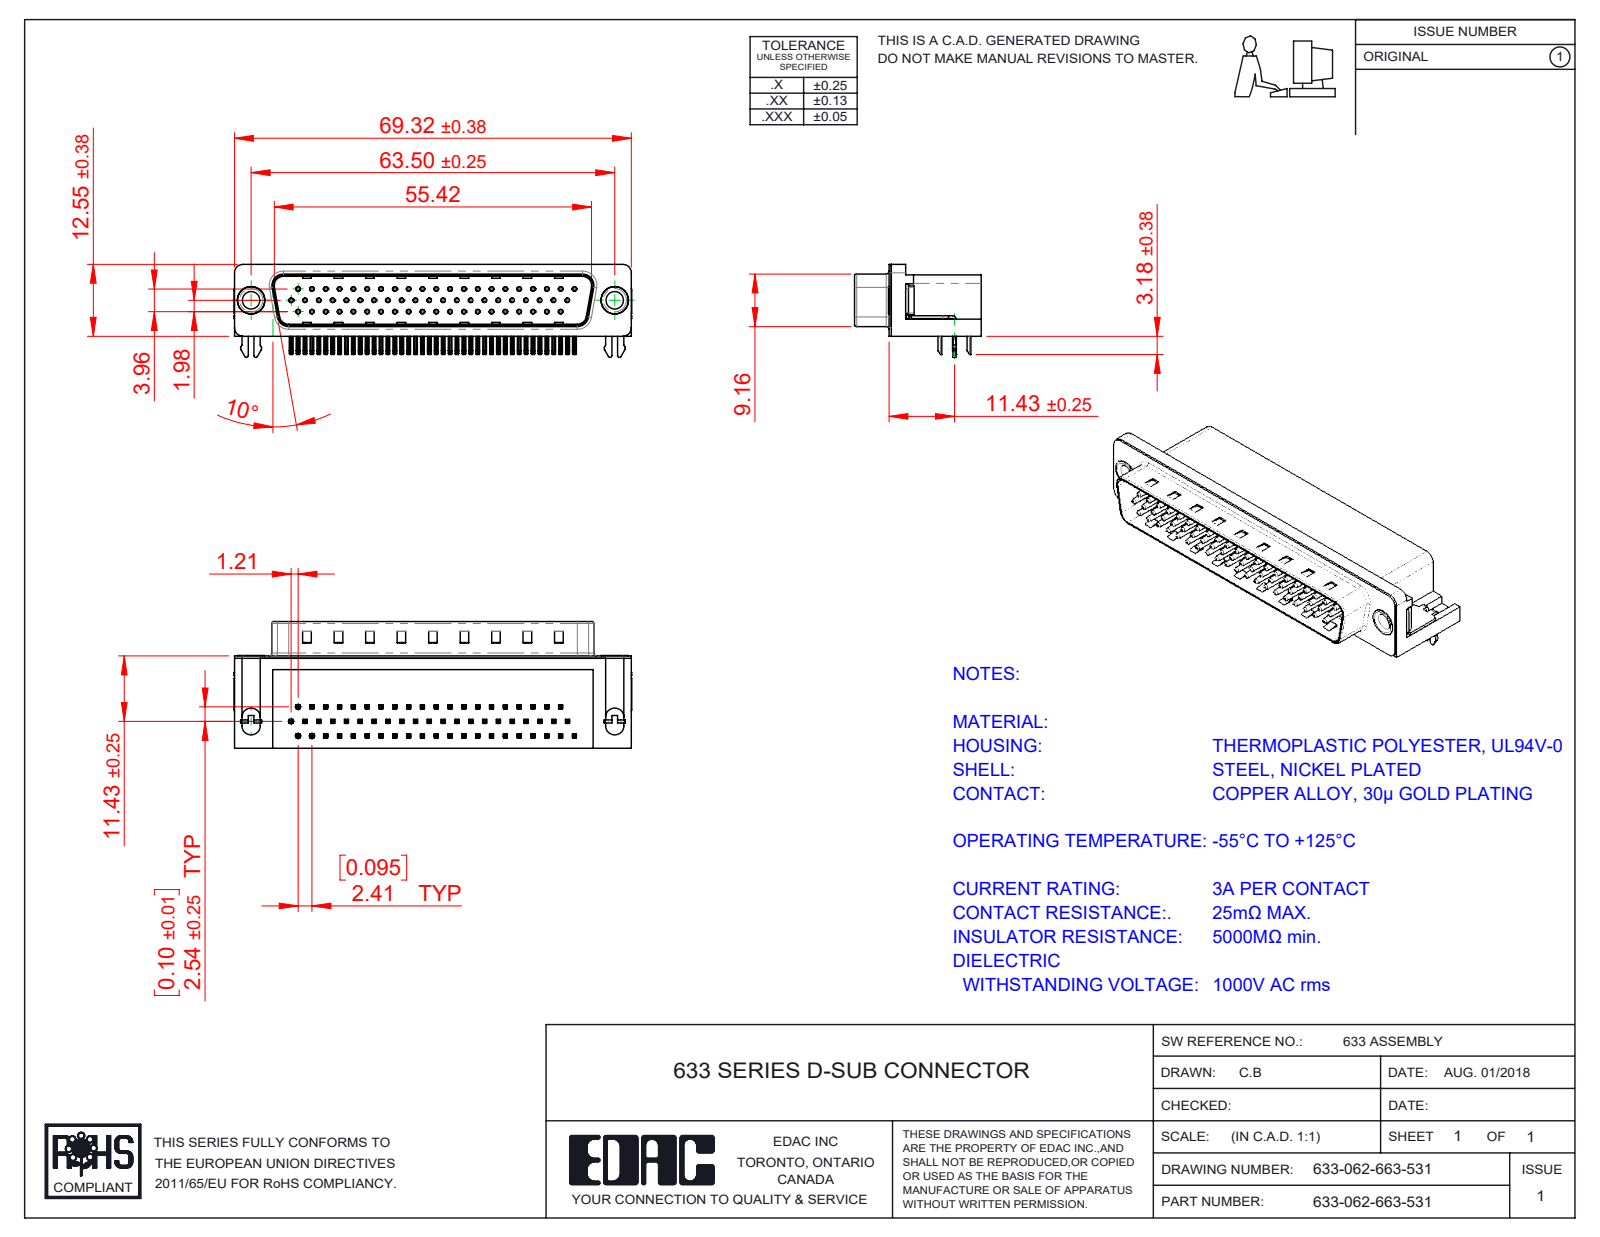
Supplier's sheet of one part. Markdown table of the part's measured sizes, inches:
| quantity | value |
| --- | --- |
| part name | 633-062-663-531; 633 Contact Top; 633 Shell_62 Contact; 633 Contact Middle (+4 more) |
| STEP written by | SolidWorks 2016 (CONFIG_CONTROL_DESIGN) |
| units | inches |
| bodies | 68 solids, 5076 faces (3245 planar, 1432 cylindrical, 399 other) |
| overall size | 2.732 × 0.87 × 0.64 |
| volume | 0.674 in³ |
| surface area | 20.76 in² |
| round holes (diameter × count) | 0.014 × 62, 0.031 × 62, 0.12 × 2, 0.157 × 2, 0.189 × 2, 0.197 × 2 |
| round bosses / shafts (diameter × count) | 0.03 × 62, 0.193 × 2, 0.187 × 2, 0.152 × 2 |
| partial cylindrical surfaces (radius × count) | 0.01 × 256, 0.005 × 124, 0.039 × 16, 0.02 × 14, 0.063 × 8, 0.059 × 7, 0.013 × 4, 0.035 × 4 |
| main face-to-face distances | 0.016, 0.407, 0.618, 0.345, 0.114, 0.098, 0.1, 0.083, 0.329, 0.412 |
| hole center spacings | 0.095, 0.19, 0.285, 0.38, 0.57, 0.665, 0.19, 0.285 |
